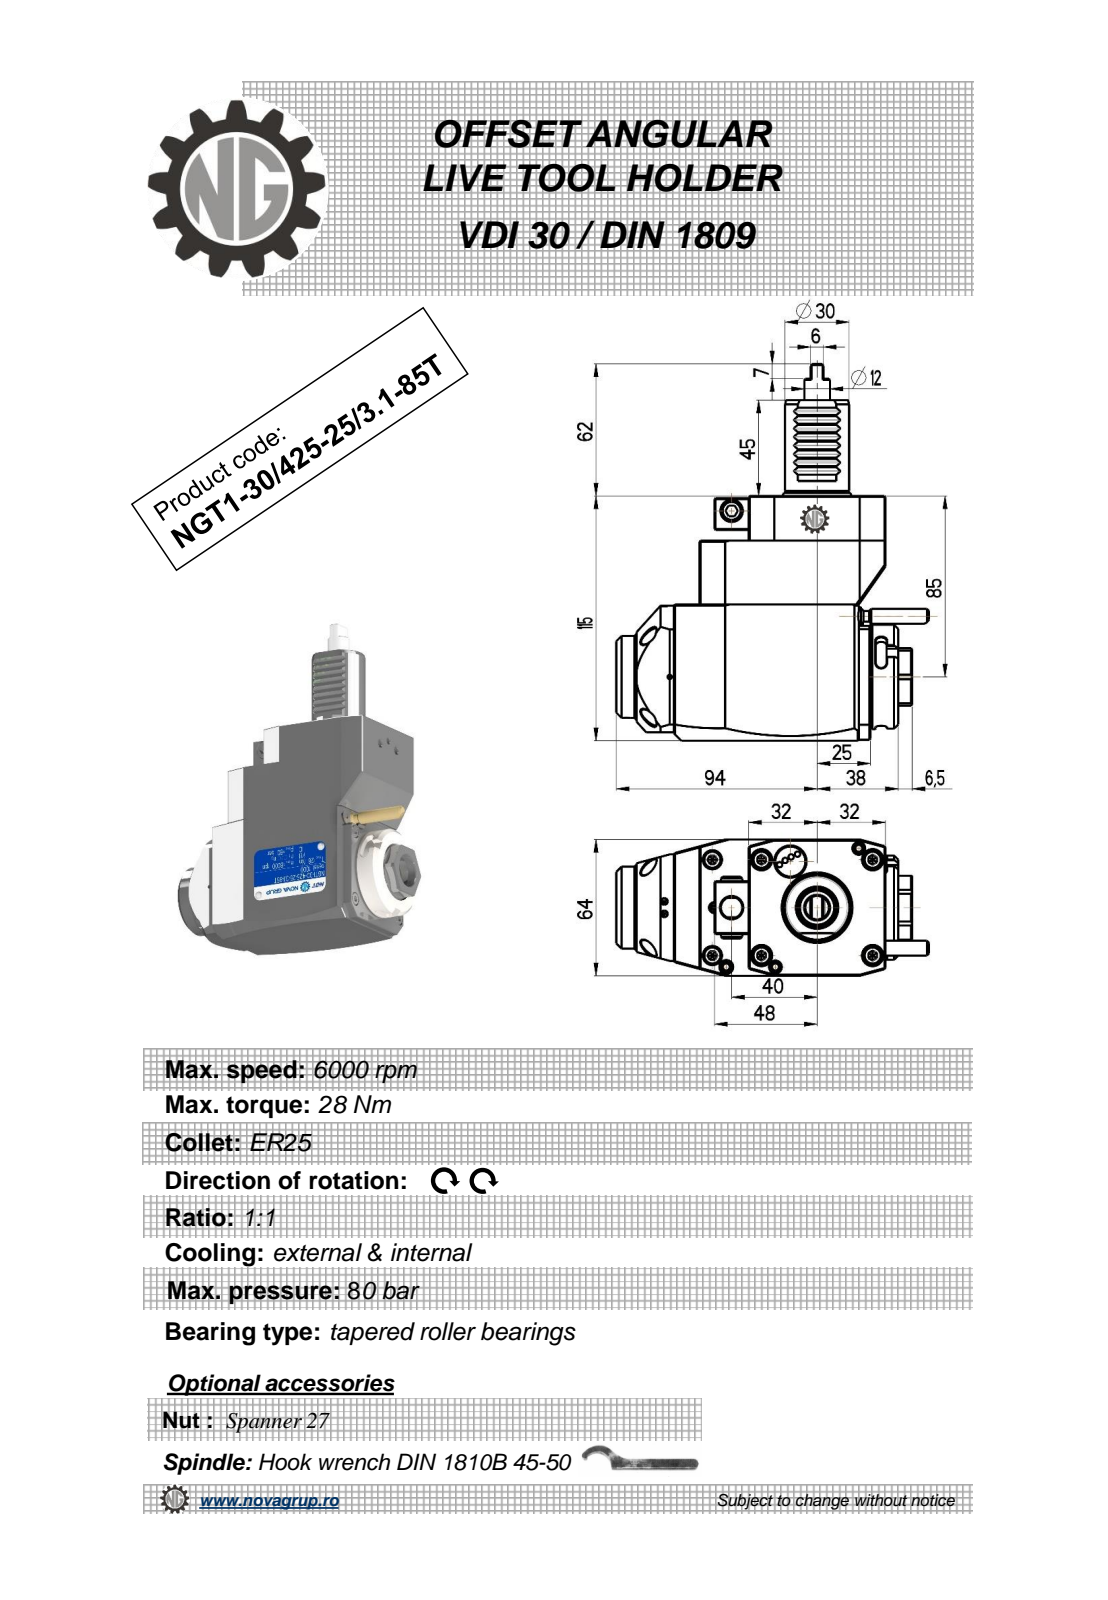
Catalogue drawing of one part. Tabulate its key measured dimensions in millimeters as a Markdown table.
| quantity | value |
| --- | --- |
| part name | NGT1_30_425_25_3_1_85T |
| STEP written by | PRO/ENGINEER BY PARAMETRIC TECHNOLOGY CORPORATION, 2010280 (CONFIG_CONTROL_DESIGN) |
| units | millimeters |
| bodies | 1 solid, 331 faces (189 planar, 70 cylindrical, 72 other) |
| overall size | 177 × 146.38 × 64 |
| volume | 716 749 mm³ |
| surface area | 59 494 mm² |
| round holes (diameter × count) | 2.5 × 1, 3 × 1, 8.5 × 1, 9.5 × 1, 10 × 1, 18 × 1 |
| round bosses / shafts (diameter × count) | 8.96 × 2, 49 × 1, 42 × 1, 38.5 × 1, 30 × 1, 12 × 1, 10 × 1, 7 × 1 |
| partial cylindrical surfaces (radius × count) | 0.3 × 8, 2.5 × 6, 0.8 × 2, 180 × 2, 4.5 × 1, 15 × 1, 21.5 × 1, 33.5 × 1 |
| main face-to-face distances | 64, 115, 7, 80, 87, 6, 94, 21, 12.5, 13 |
| hole center spacings | 34.25, 51.62, 76.5 |
